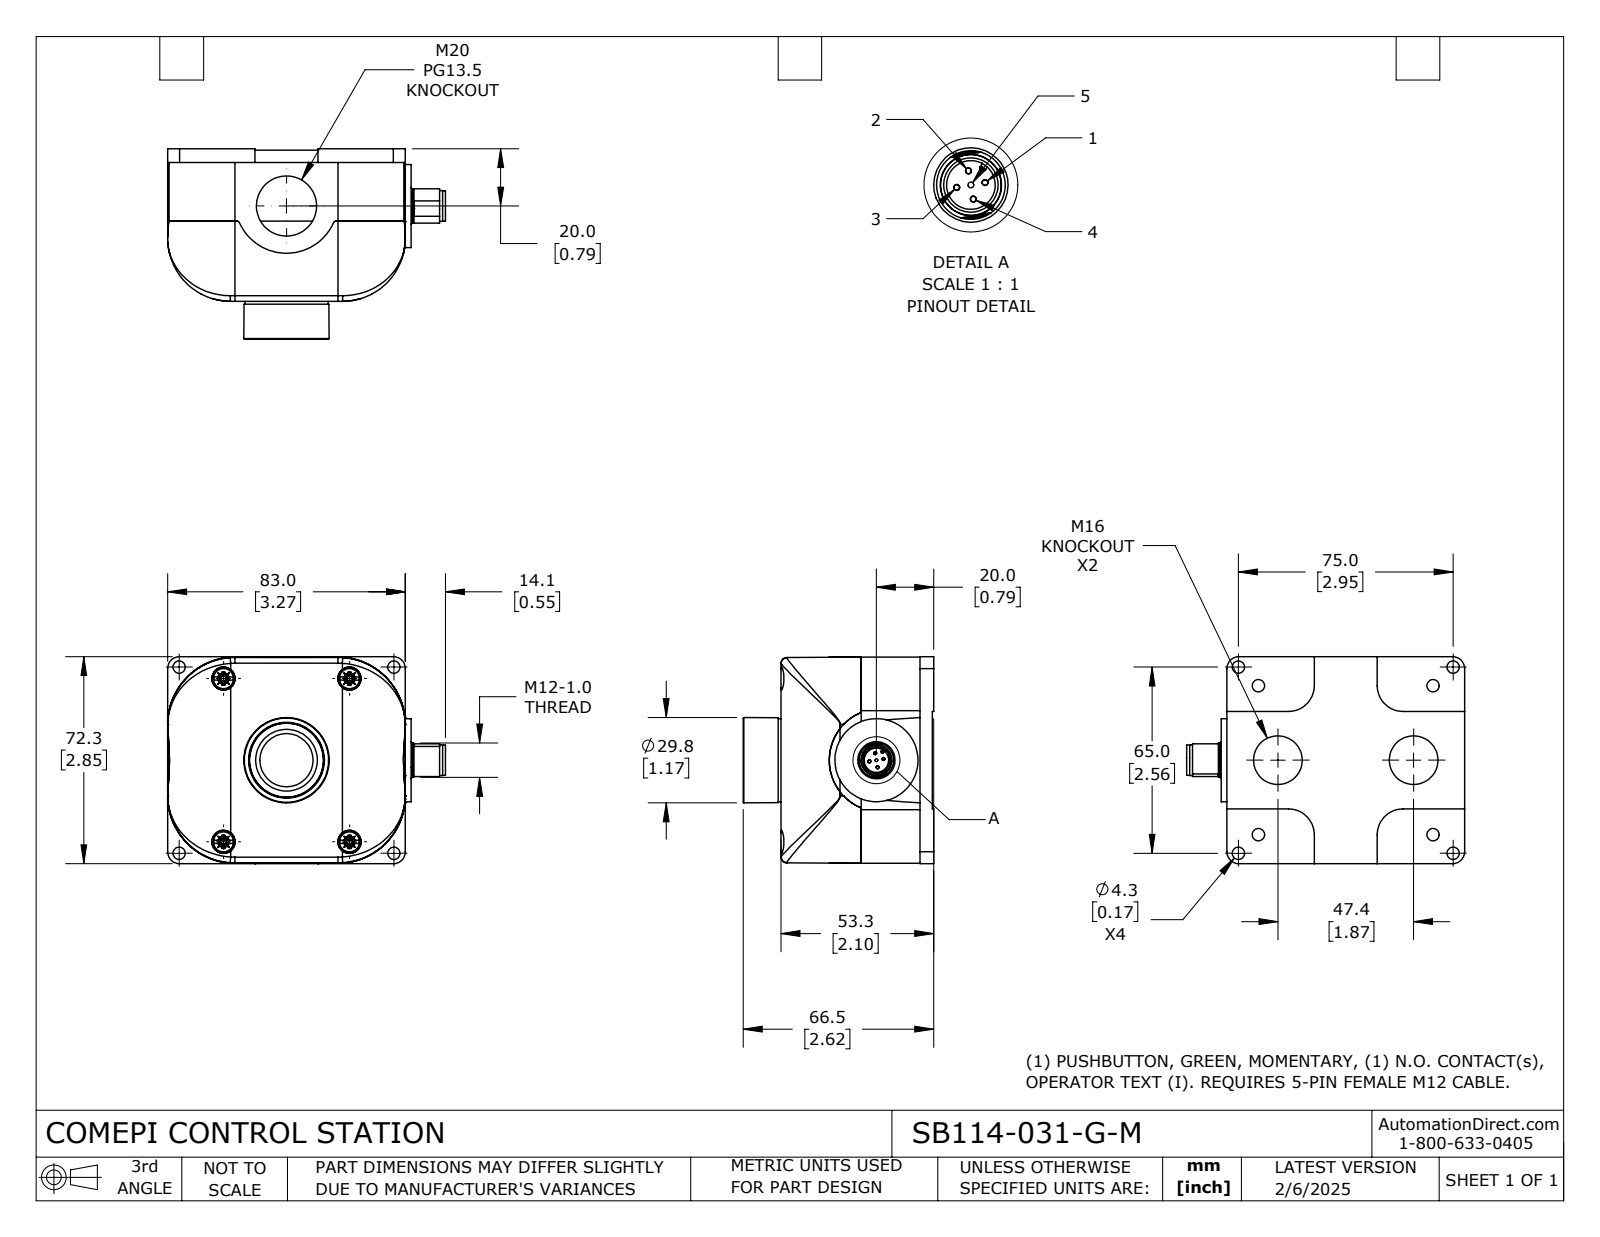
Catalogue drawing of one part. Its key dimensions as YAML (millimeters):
part_name: "SB114-031-G-M"
step_written_by: "SolidWorks 2024 (CONFIG_CONTROL_DESIGN)"
units: millimeters
bodies: {solids: 10, faces: 786, planar: 370, cylindrical: 273, other: 143}
overall_size: [97.1, 72.3, 66.5]
volume: 216800
surface_area: 61500
round_holes:
  - {diameter: 4.3, count: 8}
  - {diameter: 1, count: 4}
  - {diameter: 1.7, count: 4}
  - {diameter: 2.2, count: 4}
  - {diameter: 8.2, count: 4}
  - {diameter: 17, count: 2}
  - {diameter: 21, count: 2}
  - {diameter: 8.5, count: 1}
  - {diameter: 13.5, count: 1}
  - {diameter: 18.1, count: 1}
  - {diameter: 21.7, count: 1}
round_bosses_or_shafts:
  - {diameter: 1, count: 5}
  - {diameter: 7, count: 4}
  - {diameter: 2.2, count: 4}
  - {diameter: 1.7, count: 4}
  - {diameter: 29, count: 2}
  - {diameter: 0.6, count: 2}
  - {diameter: 26.4, count: 1}
  - {diameter: 25.8, count: 1}
partial_cylinders:
  - {radius: 0.5, count: 5}
  - {radius: 0.9, count: 4}
  - {radius: 2, count: 4}
  - {radius: 9, count: 4}
  - {radius: 9.7, count: 4}
  - {radius: 23.5, count: 4}
  - {radius: 0.2, count: 2}
  - {radius: 0.3, count: 2}
face_to_face_distances: [24.8, 2.5, 22.3, 52.8, 50.3, 28, 3, 53.3, 0.5, 25.3]
hole_center_spacings: [9.6, 26.9, 35.3, 40.1, 49.6, 58.9, 60.1, 68.3]
